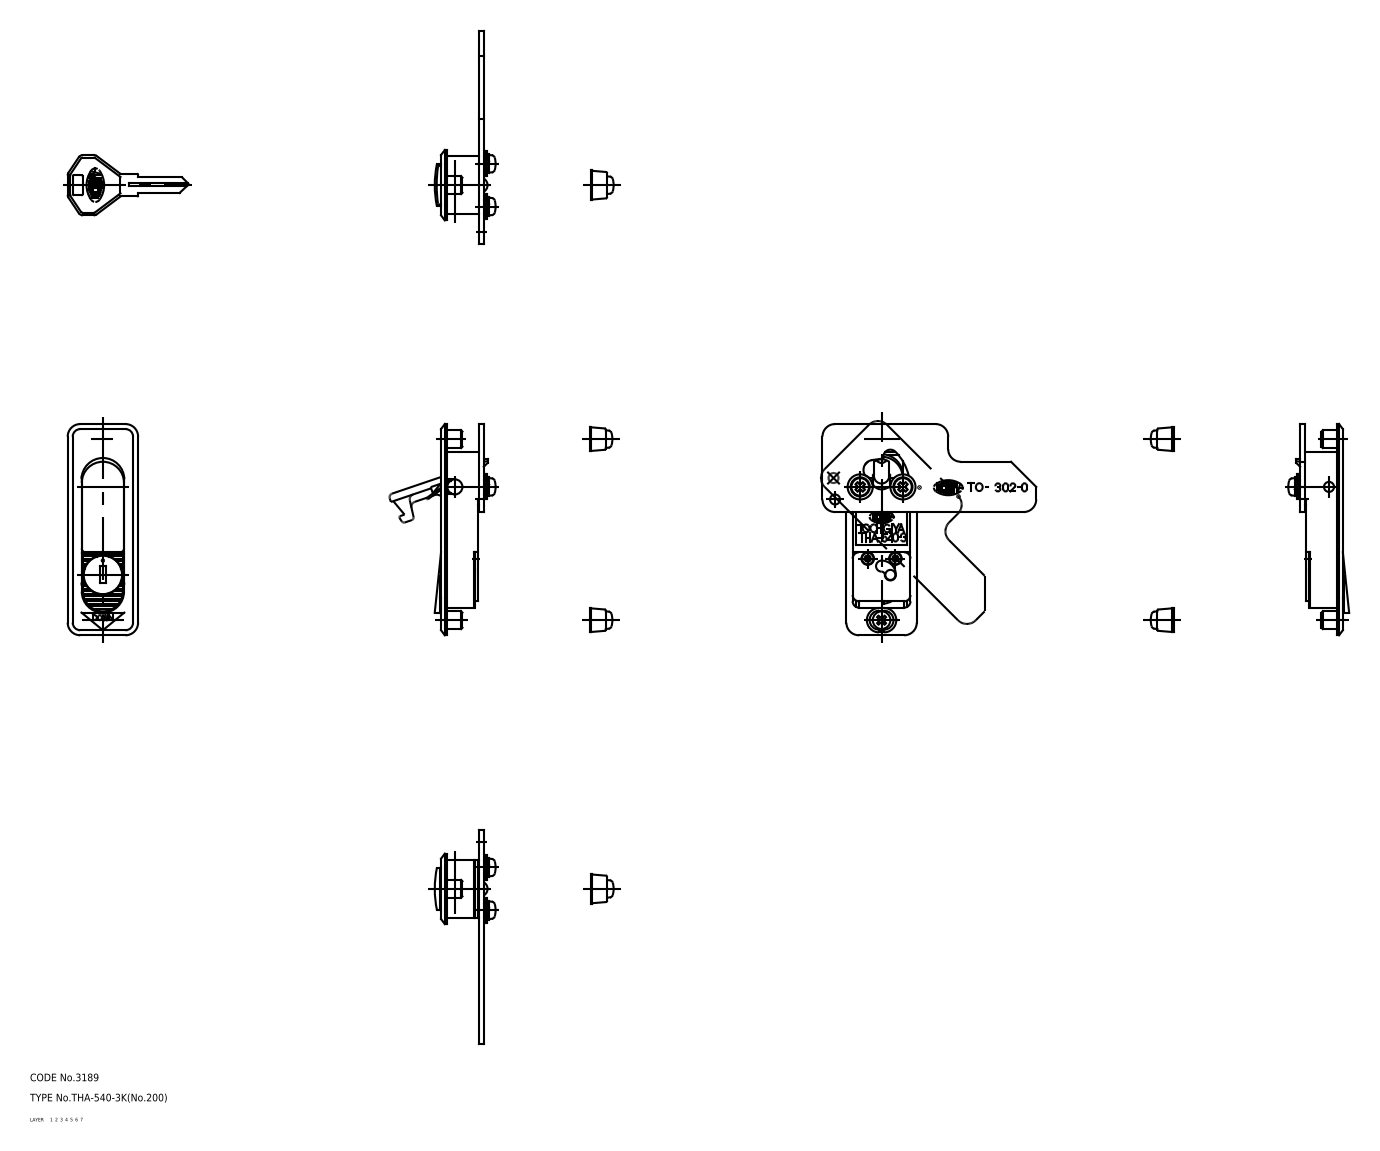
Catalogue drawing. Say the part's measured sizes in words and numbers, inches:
The part is named "screw_B; screw_A; bracket; latch (+6 more)". Its 3-D file was written by "CADfix (AUTOMOTIVE_DESIGN)". It is 12 solids with 492 faces: 0 planar, 0 cylindrical and 492 other. Overall it measures 4.269 by 3.346 by 3.307 inches. Its volume is 1.413 cubic inches and its surface area 35.8 square inches.
